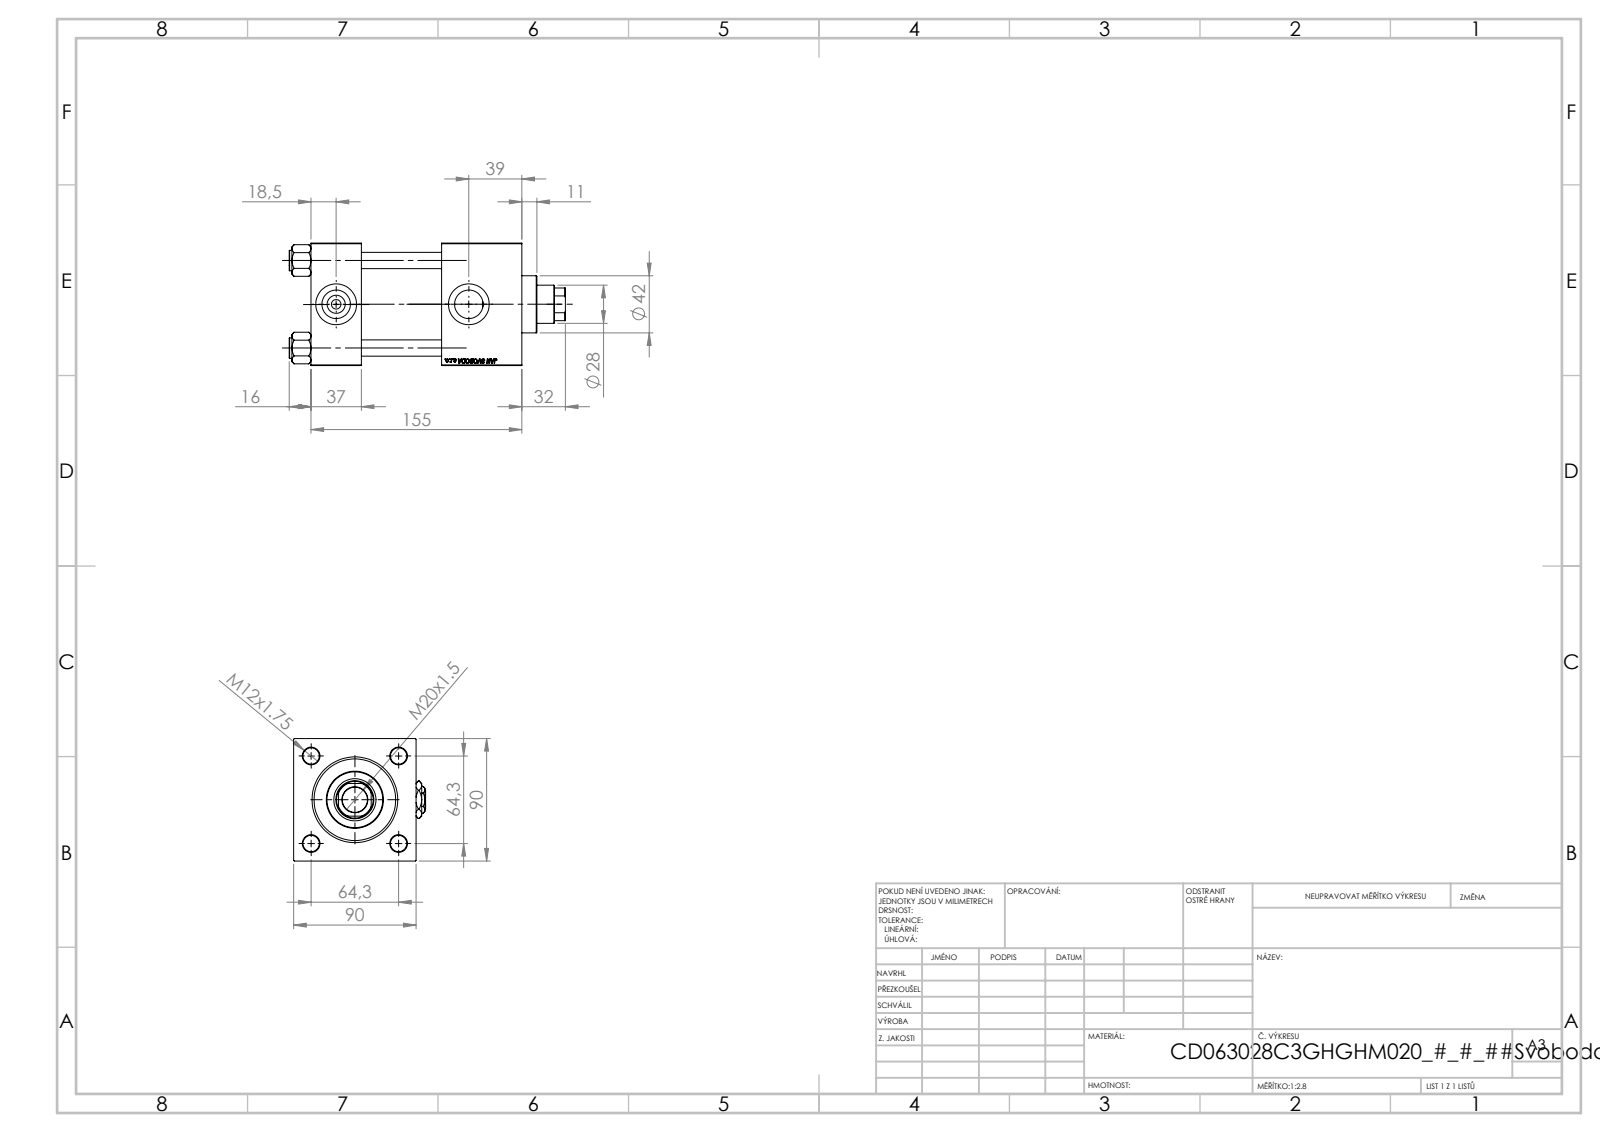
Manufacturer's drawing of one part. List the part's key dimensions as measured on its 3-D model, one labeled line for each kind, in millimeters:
Part name (STEP PRODUCT): V215CD_VCP_C; V215CD_C_TYCINKA; Zatka_pro_OIL_PORT; NUT_M5_V215CD_C (+2 more)
STEP written by: SolidWorks 2019 (CONFIG_CONTROL_DESIGN)
Units: millimetres
Bodies: 13 solids, 1250 faces (574 planar, 98 cylindrical, 578 other)
Overall size (bounding box): 203 × 97 × 90
Volume: 940 483 mm³ · Surface area: 183 915 mm²
Round holes (diameter × count): ⌀12 ×4, ⌀7 ×2, ⌀20.96 ×2, ⌀30 ×2, ⌀18.5 ×1, ⌀28 ×1, ⌀31 ×1, ⌀50 ×1, ⌀60 ×1, ⌀63 ×1
Round bosses / shafts (diameter × count): ⌀15 ×4, ⌀69 ×1, ⌀42 ×1
Partial cylindrical surfaces — rounded edges, fillets, slot ends (radius × count): R13.5 ×1
Main face-to-face distances: 90, 59, 37, 118, 155, 96, 126.3, 89.3, 30.3, 28.7
Hole centre spacings: 45.47, 64.3, 90.93, 97.5
